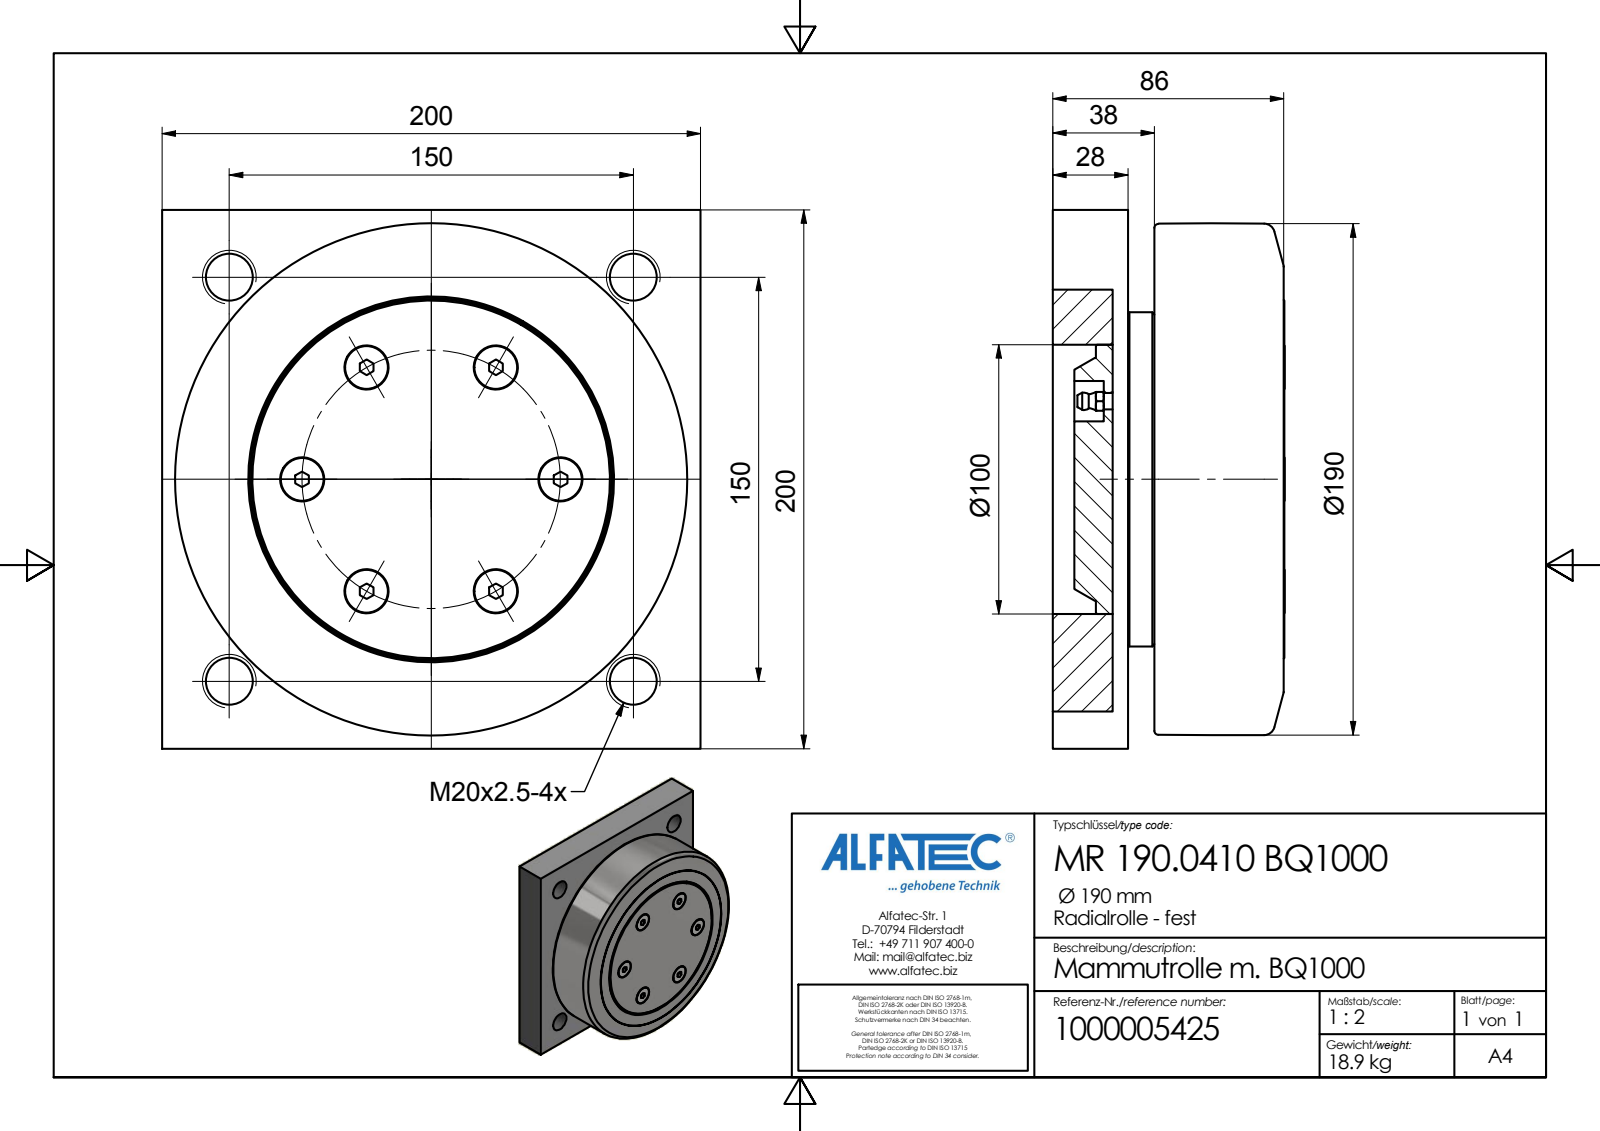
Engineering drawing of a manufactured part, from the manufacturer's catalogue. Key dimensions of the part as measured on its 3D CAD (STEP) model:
Part name (STEP PRODUCT): MR 190.0410 BQ1000_Kontur
STEP written by: Autodesk Inventor 2020 (AUTOMOTIVE_DESIGN)
Units: millimetres
Bodies: 1 solid, 180 faces (79 planar, 43 cylindrical, 58 other)
Overall size (bounding box): 200 × 200 × 86.15
Volume: 2 200 000 mm³ · Surface area: 255 242 mm²
Round holes (diameter × count): ⌀8.5 ×6, ⌀17.29 ×4, ⌀2.5 ×1, ⌀4.92 ×1, ⌀15 ×1, ⌀100 ×1, ⌀109.9 ×1, ⌀134.7 ×1, ⌀146 ×1
Round bosses / shafts (diameter × count): ⌀16 ×6, ⌀8 ×6, ⌀133.7 ×1, ⌀124 ×1, ⌀120.7 ×1, ⌀110 ×1, ⌀90 ×1, ⌀3 ×1
Partial cylindrical surfaces — rounded edges, fillets, slot ends (radius × count): R3 ×1, R3.5 ×1
Main face-to-face distances: 28, 8.3, 37.8, 9.8, 86, 58, 48.2, 200, 39.7, 49.5
Hole centre spacings: 48, 83.14, 60.98, 79.71, 104.49, 106.07, 127.24, 144.06
